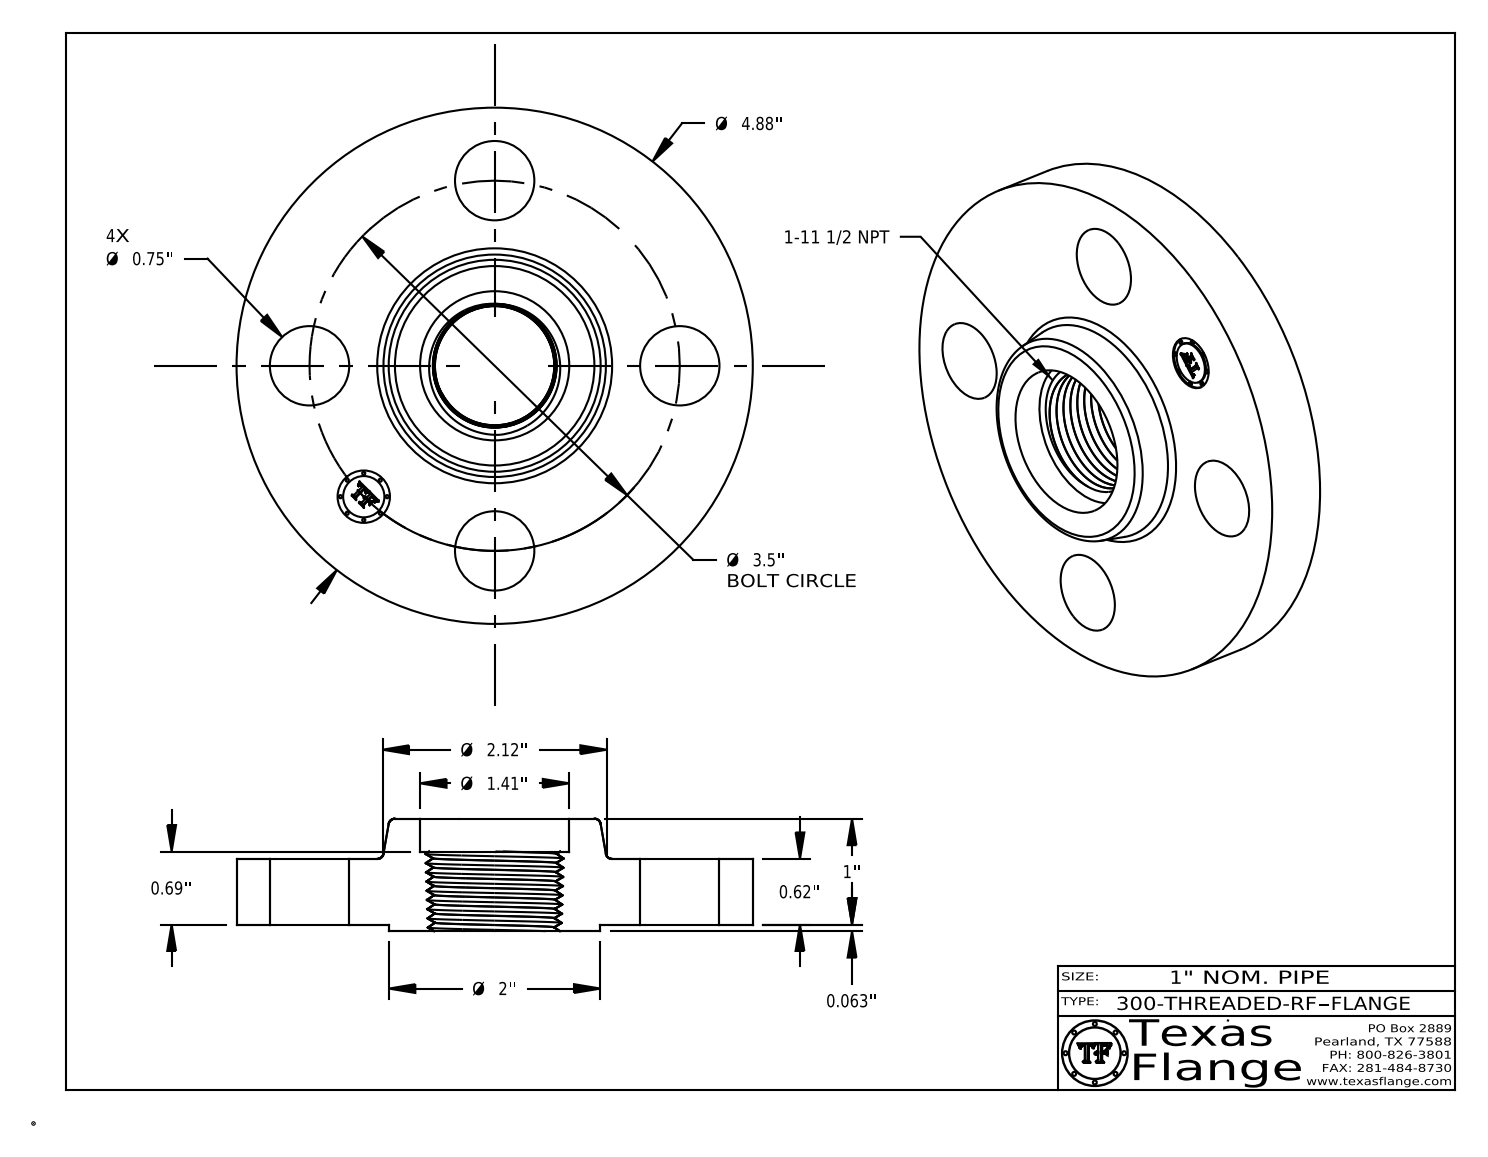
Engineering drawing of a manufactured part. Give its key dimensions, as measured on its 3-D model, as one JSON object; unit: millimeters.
{"part_name": "300-THREADED-RF", "step_written_by": "CATIA V5 STEP AP214 (AUTOMOTIVE_DESIGN)", "units": "millimeters", "bodies": {"solids": 1, "faces": 503, "planar": 370, "cylindrical": 34, "other": 99}, "overall_size": [124, 124, 27], "volume_mm3": 173700, "surface_area_mm2": 36110, "round_holes": [[19.1, 4], [12.6, 1], [35.8, 1]], "round_bosses_or_shafts": [[0.8, 8], [124, 1], [50.8, 1], [9.9, 1]], "face_to_face_distances": [15.7, 1.6, 17.3, 27, 25.4, 9.7, 1.8, 19.1, 17.5, 7.9], "hole_center_spacings": [44.5, 62.9, 34, 82.1, 88.9]}
